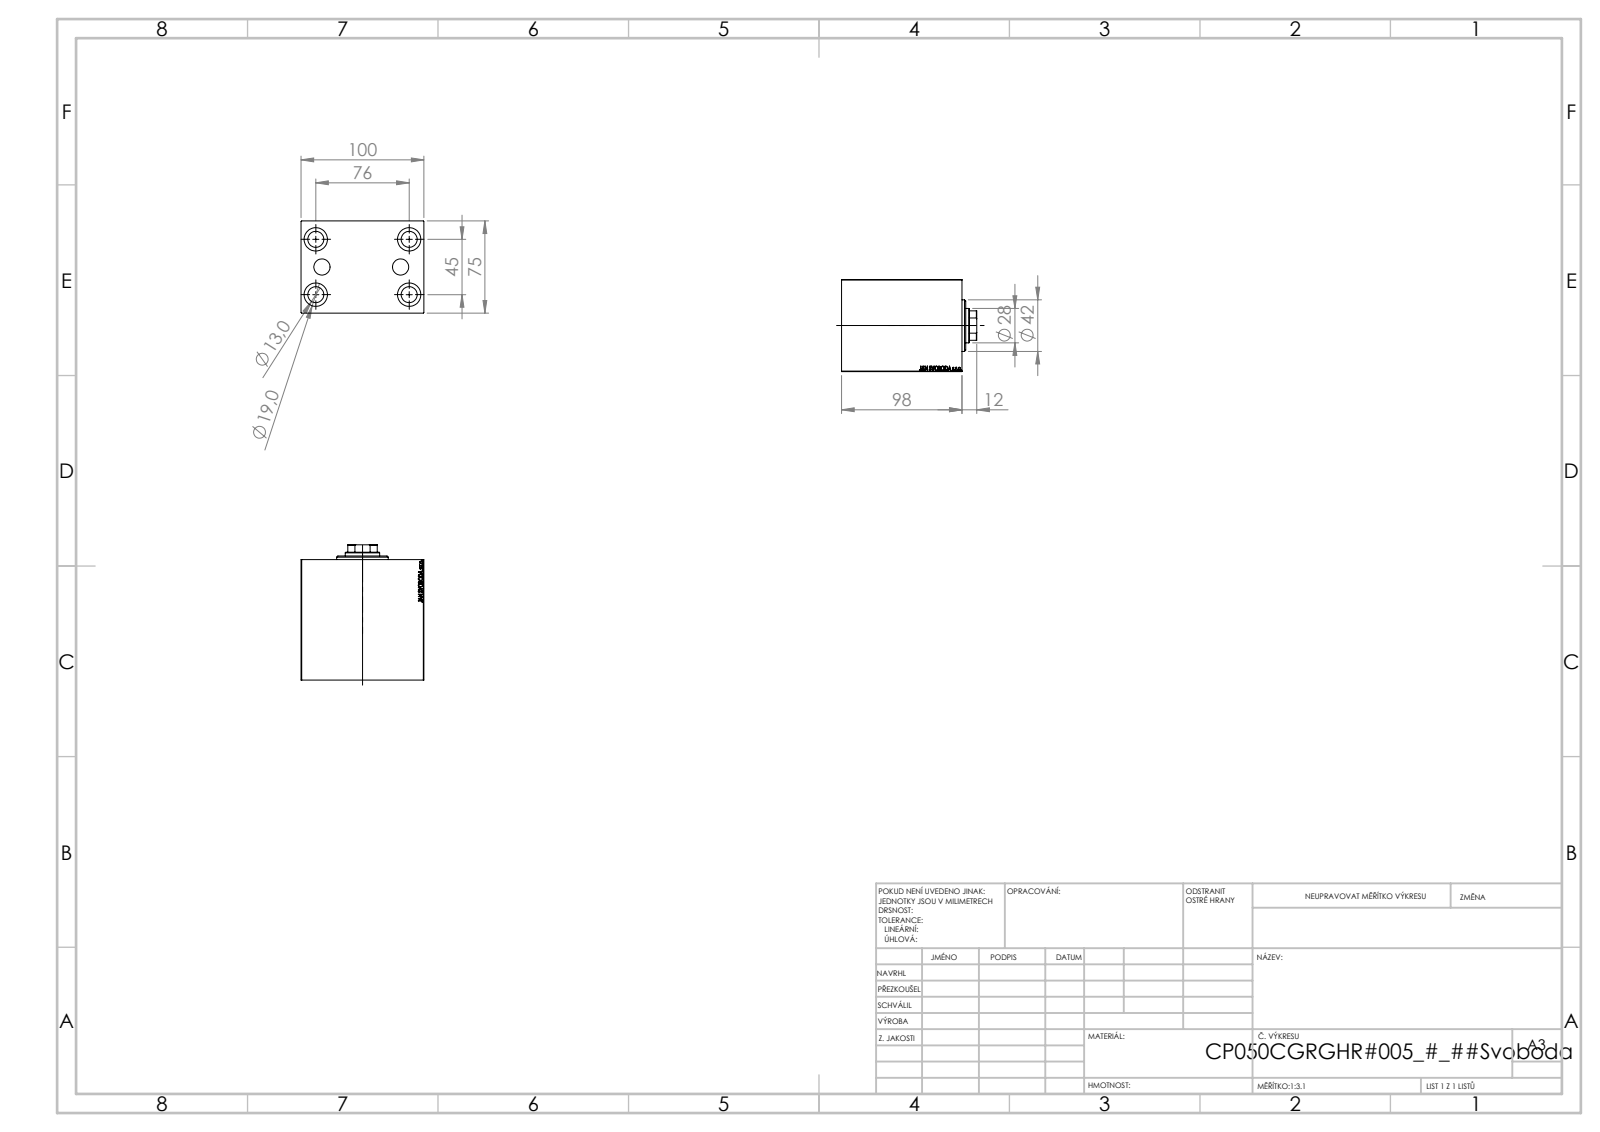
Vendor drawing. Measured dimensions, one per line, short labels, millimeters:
name: V450CP_VC_B; V450CP_C; V450CP_B_VCP
written by: SolidWorks 2019 (CONFIG_CONTROL_DESIGN)
unit: mm
bodies: 3 solids, 878 faces (412 planar, 68 cylindrical, 398 other)
size: 110 × 100 × 75
volume: 657 875 mm³; area: 113 856 mm²
holes: 4× ⌀13, 4× ⌀19, 2× ⌀4, 2× ⌀9.73, 2× ⌀13.16, 2× ⌀15, 1× ⌀18.5, 1× ⌀28, 1× ⌀31.5, 1× ⌀32.5, 1× ⌀50, 1× ⌀52
bosses: 1× ⌀42
rounds: 1× R13.5
face distances: 75, 100, 98, 49, 14, 84, 44, 5, 35, 30
hole spacings: 44.16, 23.05, 23.56, 45, 72.58, 74.48, 76, 88.32
